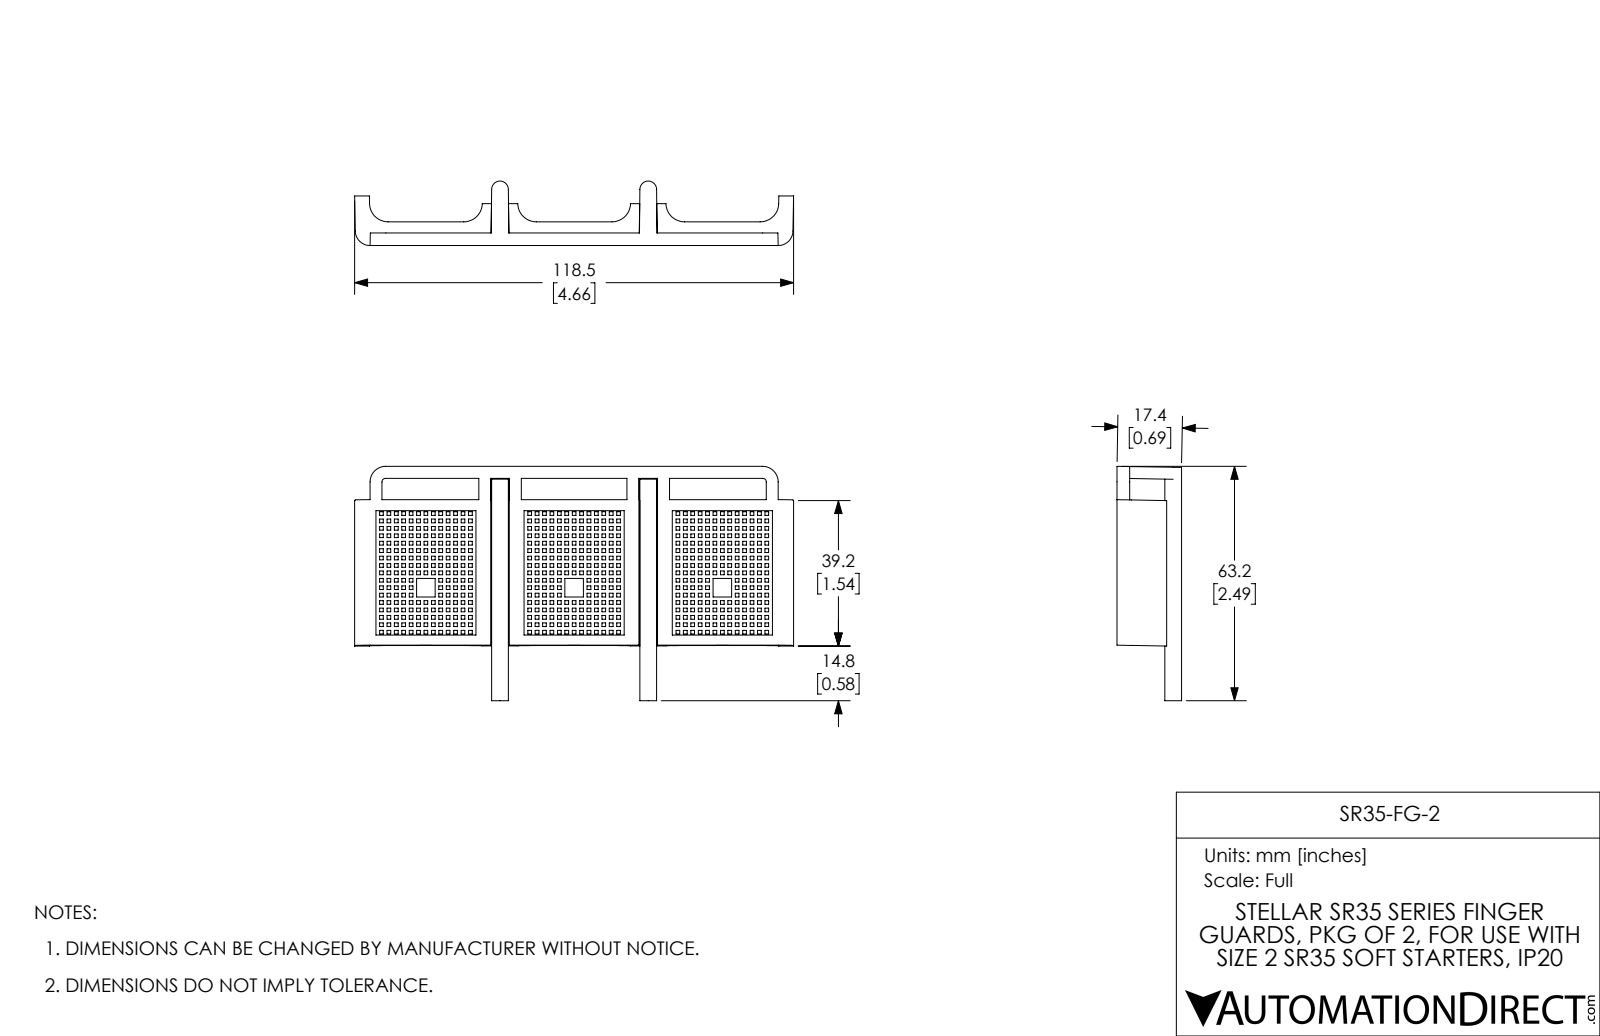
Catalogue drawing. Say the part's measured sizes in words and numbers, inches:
The part is named "STP-AGY-008-V01 (AGY2 Finger)". Its 3-D file was written by "SolidWorks 2017 (AUTOMOTIVE_DESIGN)". It is 1 solid with 2676 faces: 2656 planar, 20 cylindrical and 0 other. Overall it measures 4.664 by 2.49 by 0.685 inches. Its volume is 1.128 cubic inches and its surface area 32.72 square inches. Round bosses or shafts: 2 of diameter 0.177. Partial cylindrical surfaces (rounded edges, fillets, slot ends): 6 of radius 0.197, 4 of radius 0.039, 2 of radius 0.157, 2 of radius 0.165. The main face-to-face distances are 0.039, 0.047, 0.087, 1.575, 0.127, 3.209, 1.634, 0.118, 0.354, 1.544.
